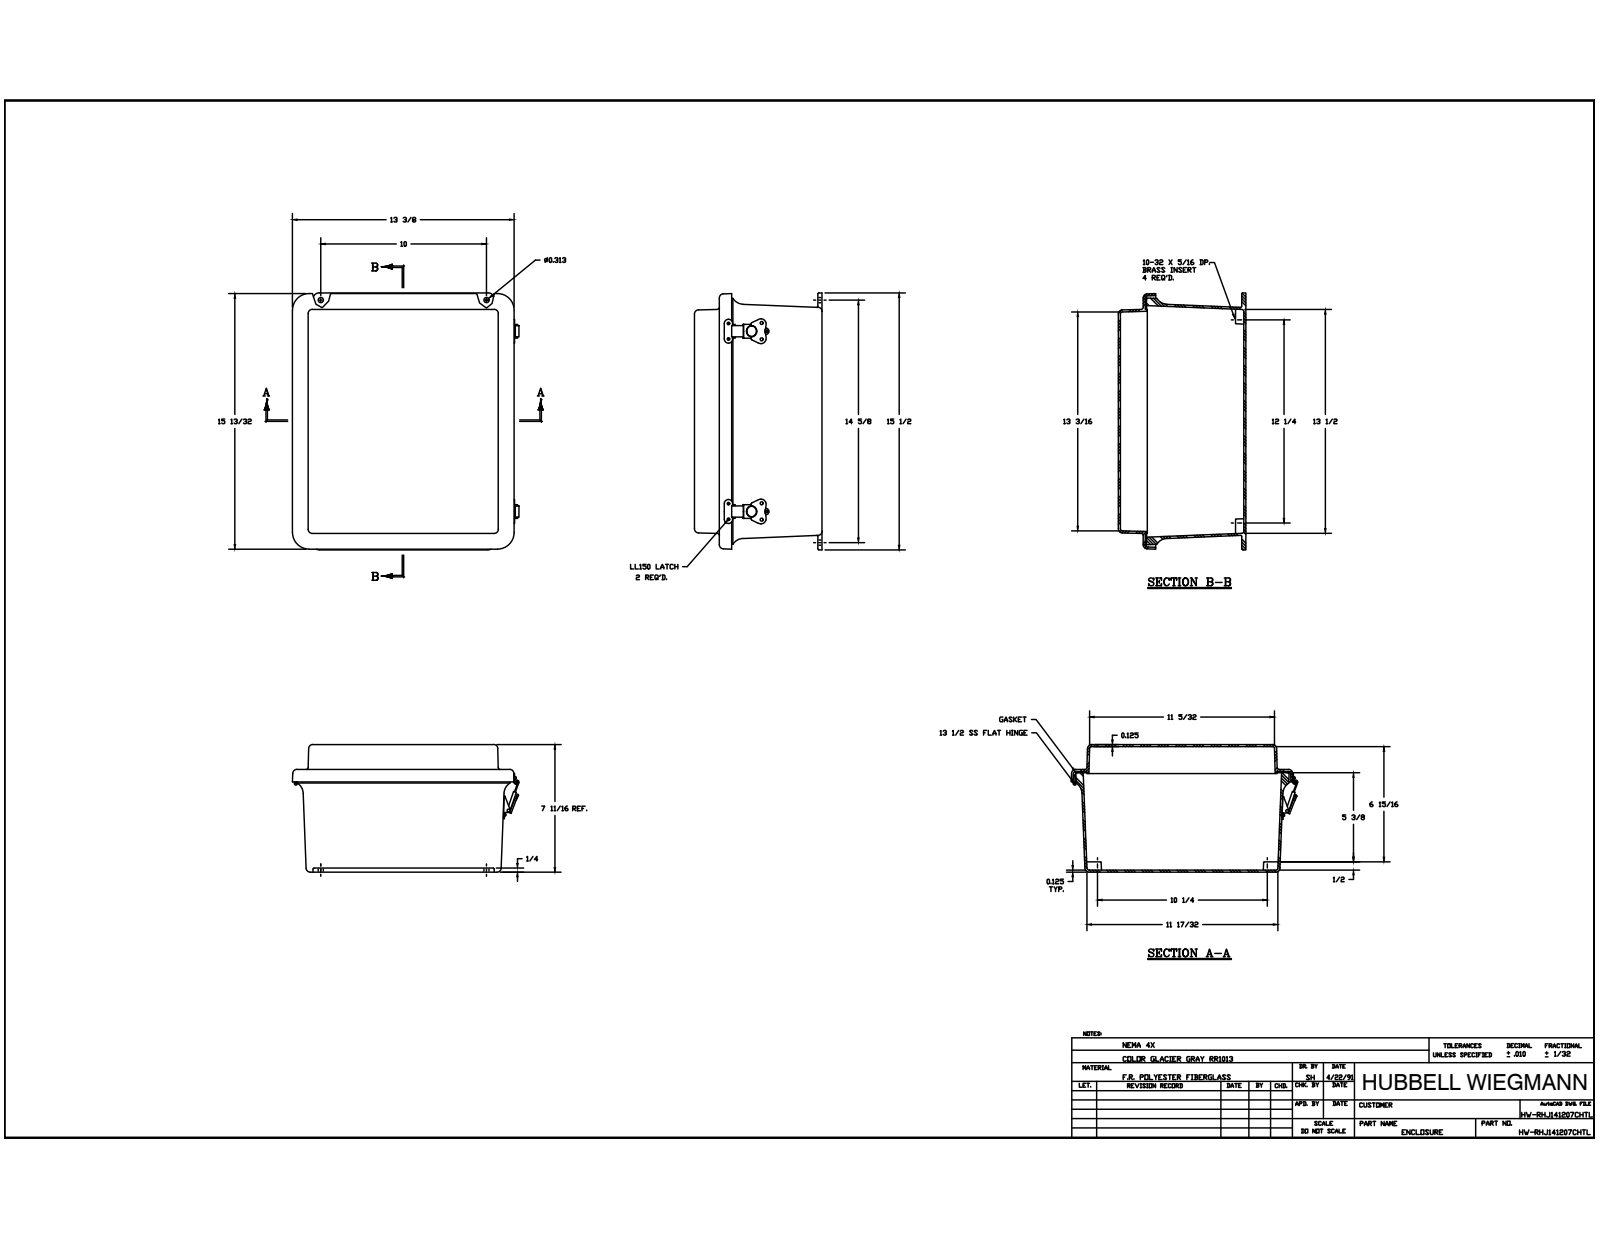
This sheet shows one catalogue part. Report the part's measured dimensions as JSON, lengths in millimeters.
{"part_name": "J1412HL_5; RMINS45821P_273; RMINS45821P_274; RMINS45821P_275 (+8 more)", "step_written_by": "Autodesk Inventor 2014 (AUTOMOTIVE_DESIGN)", "units": "millimeters", "bodies": {"solids": 50, "faces": 1279, "planar": 570, "cylindrical": 492, "other": 217}, "overall_size": [393.7, 344.94, 195.65], "volume_mm3": 1957000, "surface_area_mm2": 1123000, "round_holes": [[3.56, 18], [3.33, 10], [3.86, 8], [3.3, 4], [3.96, 4], [4.2, 4], [5, 4], [5.54, 4], [3, 2], [3.5, 2], [4.61, 2], [4.62, 2]], "round_bosses_or_shafts": [[6.35, 18], [3.17, 18], [6.86, 4], [14.8, 2], [13.3, 2], [5.3, 2], [4.7, 2], [3.25, 2]], "partial_cylinders_radius": [[0.79, 20], [3.17, 20], [6.35, 20], [2, 19], [0.95, 8], [1, 8], [1.15, 8], [1.2, 8]], "face_to_face_distances": [3.18, 3.17, 189.3, 192.48, 195.65, 192.47, 38.1, 151.2, 154.38, 41.27], "hole_center_spacings": [82.55, 165.1, 276.4, 247.65, 6.35, 76.2, 23.83, 34.8]}
